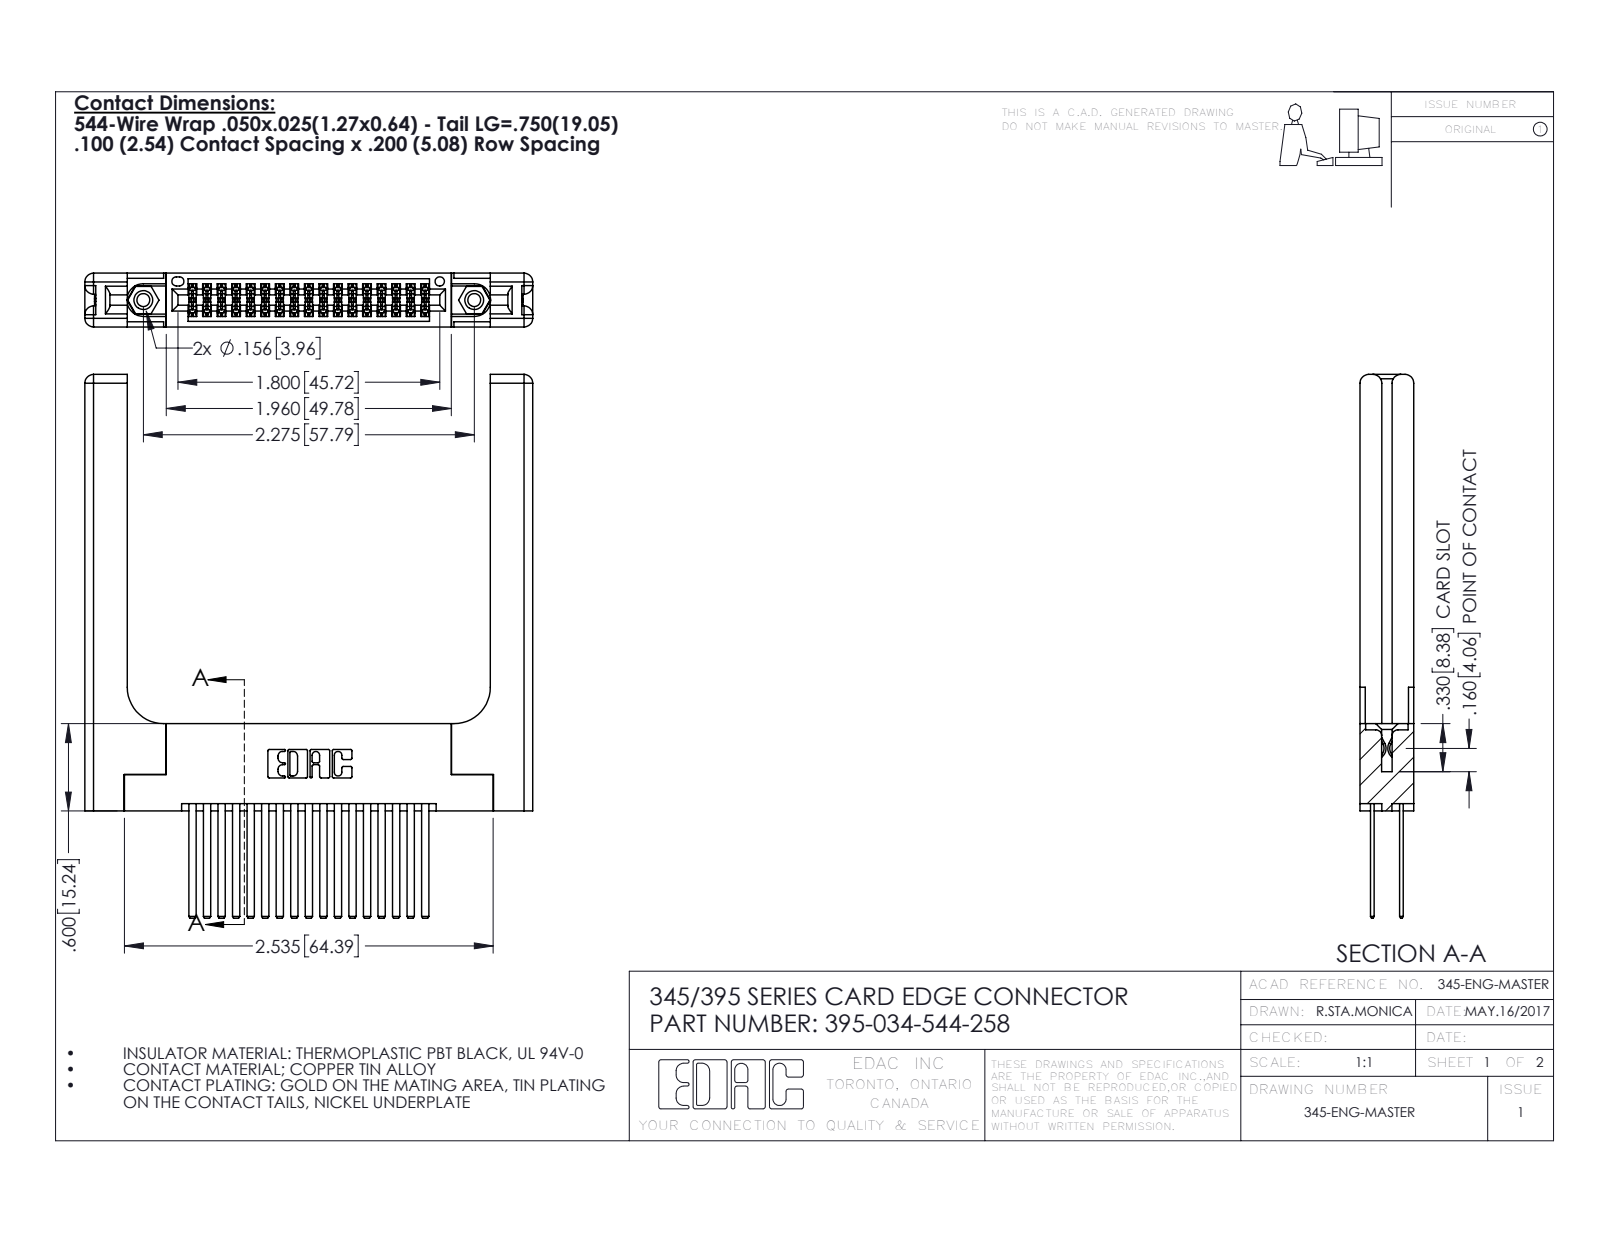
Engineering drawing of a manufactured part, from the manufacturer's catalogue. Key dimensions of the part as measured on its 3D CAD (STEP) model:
Part name (STEP PRODUCT): 345-292-001_345-293-144; 395-034-544-258; 345-250-001_345-250-001-102; 345 Part_Flush Mounting Lugs - 0.156 Dia-TH (+1 more)
STEP written by: SolidWorks 2016 (CONFIG_CONTROL_DESIGN)
Units: inches
Bodies: 39 solids, 1878 faces (1214 planar, 604 cylindrical, 60 other)
Overall size (bounding box): 3.737 × 3.079 × 0.37
Volume: 0.996 in³ · Surface area: 27.22 in²
Round holes (diameter × count): ⌀0.089 ×2, ⌀0.125 ×2, ⌀0.156 ×2, ⌀0.064 ×1
Round bosses / shafts (diameter × count): ⌀0.155 ×2
Partial cylindrical surfaces — rounded edges, fillets, slot ends (radius × count): R0.006 ×51, R0.01 ×22, R0.06 ×16, R0.007 ×6, R0.031 ×6, R0.026 ×3, R0.014 ×2, R0.019 ×2
Main face-to-face distances: 0.072, 0.298, 0.37, 0.2, 0.098, 0.272, 0.025, 0.225, 0.148, 0.15
Hole centre spacings: 0.27, 2.041, 2.275
